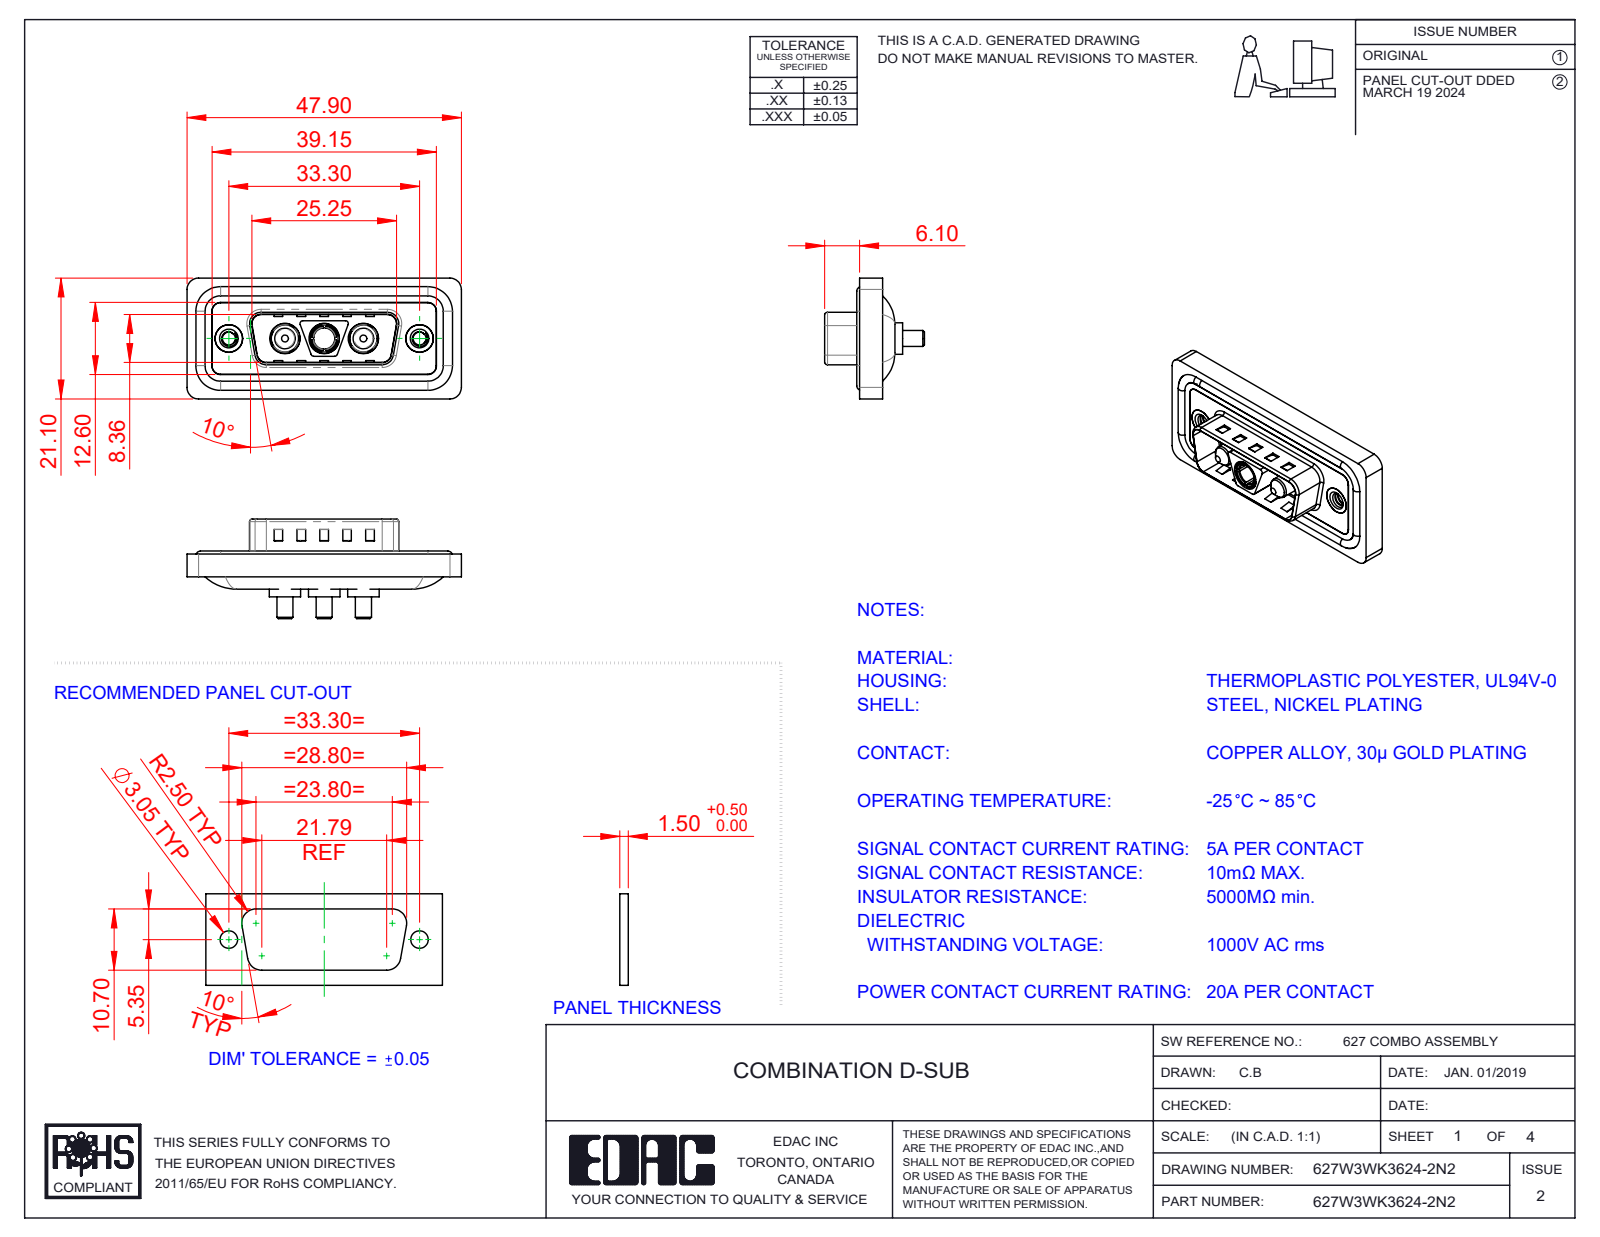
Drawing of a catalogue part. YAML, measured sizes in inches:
part_name: "627Combo Shell Front_15 Contacts; Power Pin_20A S; 627Combo Shell Rear_15 Contacts; 627Combo Housing_3WK3 (+4 more)"
step_written_by: "SolidWorks 2023 (CONFIG_CONTROL_DESIGN)"
units: inches
bodies: {solids: 13, faces: 609, planar: 231, cylindrical: 250, other: 128}
overall_size: [1.886, 0.831, 0.685]
volume: 0.347
surface_area: 14.15
round_holes:
  - {diameter: 0.191, count: 3}
  - {diameter: 0.209, count: 3}
  - {diameter: 0.089, count: 2}
  - {diameter: 0.157, count: 2}
  - {diameter: 0.189, count: 2}
  - {diameter: 0.197, count: 2}
  - {diameter: 0.146, count: 1}
round_bosses_or_shafts:
  - {diameter: 0.063, count: 4}
  - {diameter: 0.217, count: 3}
  - {diameter: 0.205, count: 3}
  - {diameter: 0.187, count: 3}
  - {diameter: 0.148, count: 3}
  - {diameter: 0.11, count: 3}
  - {diameter: 0.193, count: 2}
  - {diameter: 0.142, count: 2}
partial_cylinders:
  - {radius: 0.059, count: 26}
  - {radius: 0.079, count: 20}
  - {radius: 0.02, count: 12}
  - {radius: 0.063, count: 8}
  - {radius: 0.01, count: 4}
  - {radius: 0.024, count: 4}
  - {radius: 0.026, count: 4}
  - {radius: 0.035, count: 4}
face_to_face_distances: [0.016, 0.043, 0.059, 0.02, 0.063, 0.122, 0.114, 0.157, 0.032, 0.377]
hole_center_spacings: [0.27, 0.386, 0.656, 0.925, 0.539, 1.311]
